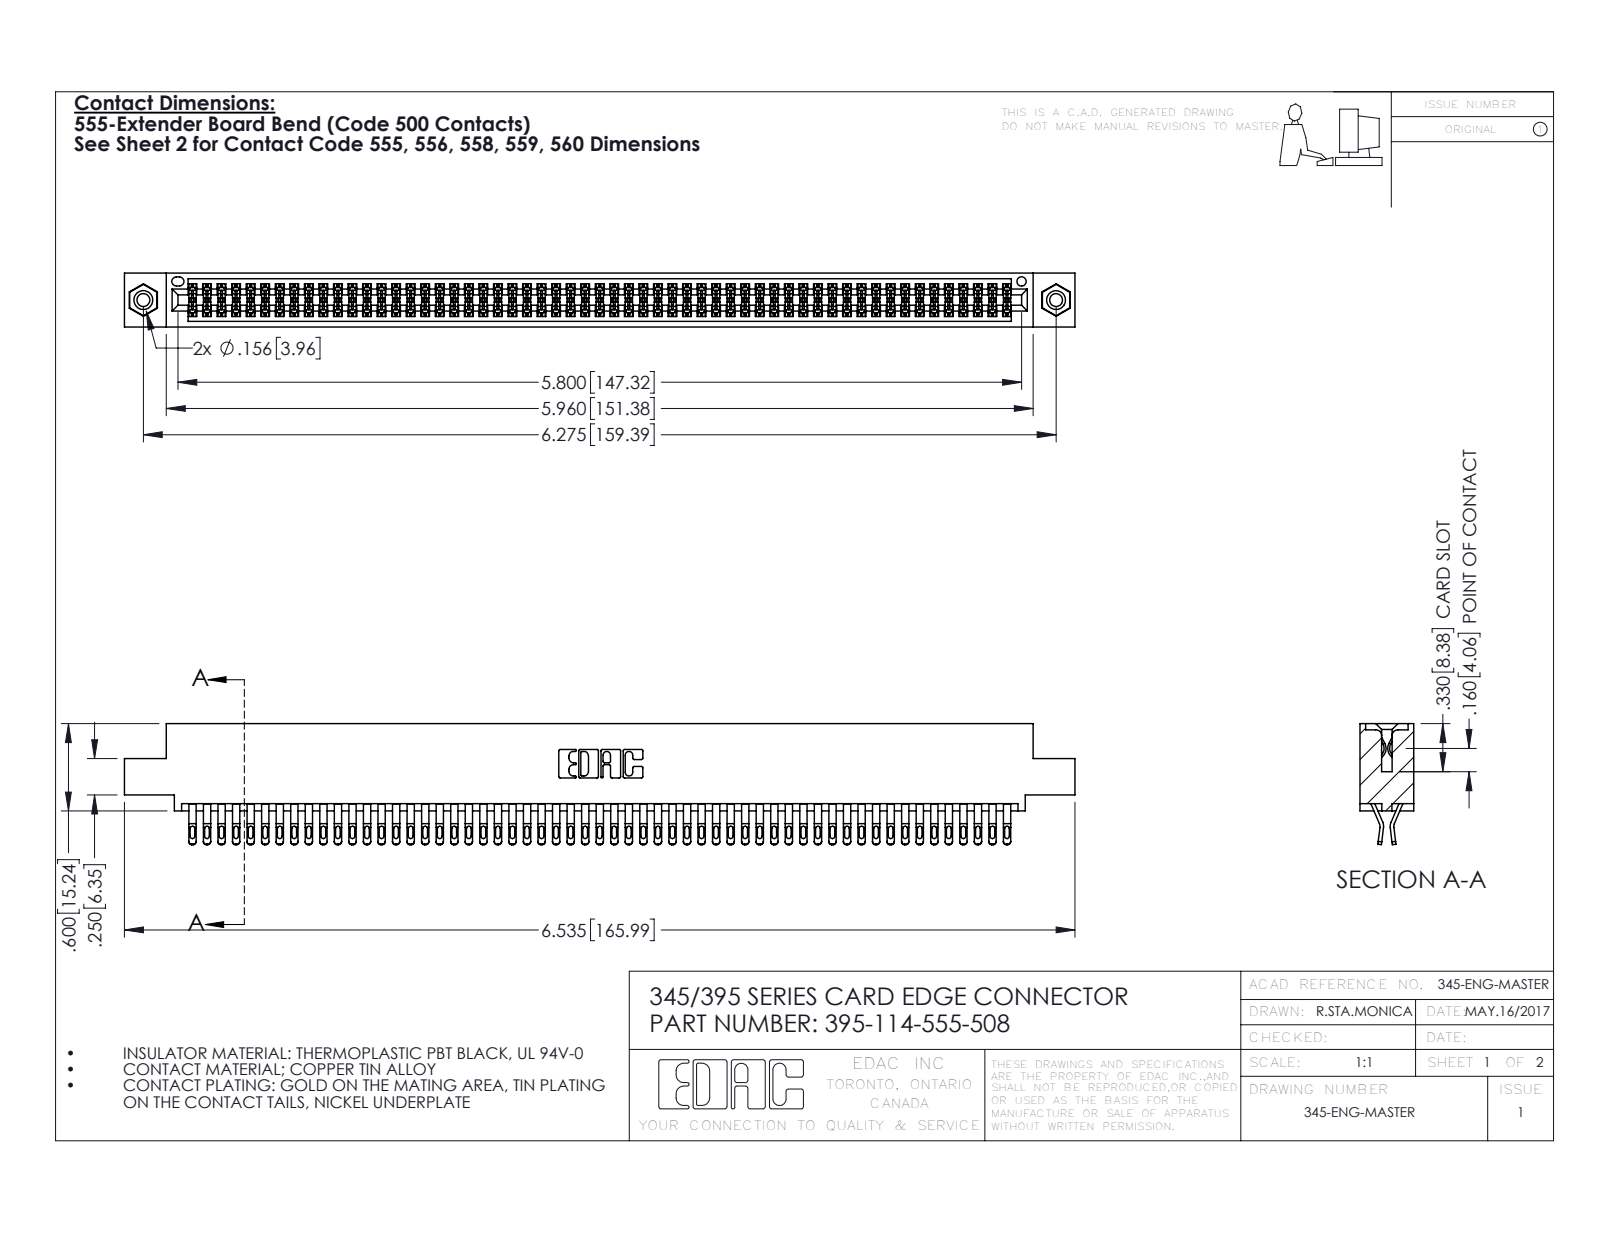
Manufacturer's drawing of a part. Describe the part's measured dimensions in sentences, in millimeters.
The part is named "345 Part_0.110 Offset - 0.156 Dia-TI; 345-250-001_345-250-003-102; 395-114-555-508; 345-292-001_555 Tail". Its 3-D file was written by "SolidWorks 2016 (CONFIG_CONTROL_DESIGN)". It is 117 solids with 6574 faces: 3650 planar, 2908 cylindrical and 16 other. Overall it measures 166 by 21.1 by 9.4 millimeters. Its volume is 16 520 cubic millimeters and its surface area 25 950 square millimeters. Round holes: 2 of diameter 2.3, 2 of diameter 3.2, 2 of diameter 4, 1 of diameter 1.6. Round bosses or shafts: 2 of diameter 3.9. Partial cylindrical surfaces (rounded edges, fillets, slot ends): 285 of radius 0.4, 228 of radius 0.5, 171 of radius 0.2, 22 of radius 0.3, 6 of radius 0.2, 6 of radius 0.8, 3 of radius 0.7, 2 of radius 0.3. The main face-to-face distances are 1.8, 7.6, 0.6, 9.4, 5.1, 2.5, 6.9, 5.7, 4.4, 3.8. The hole center spacings are 6.9, 153.4, 159.4.
